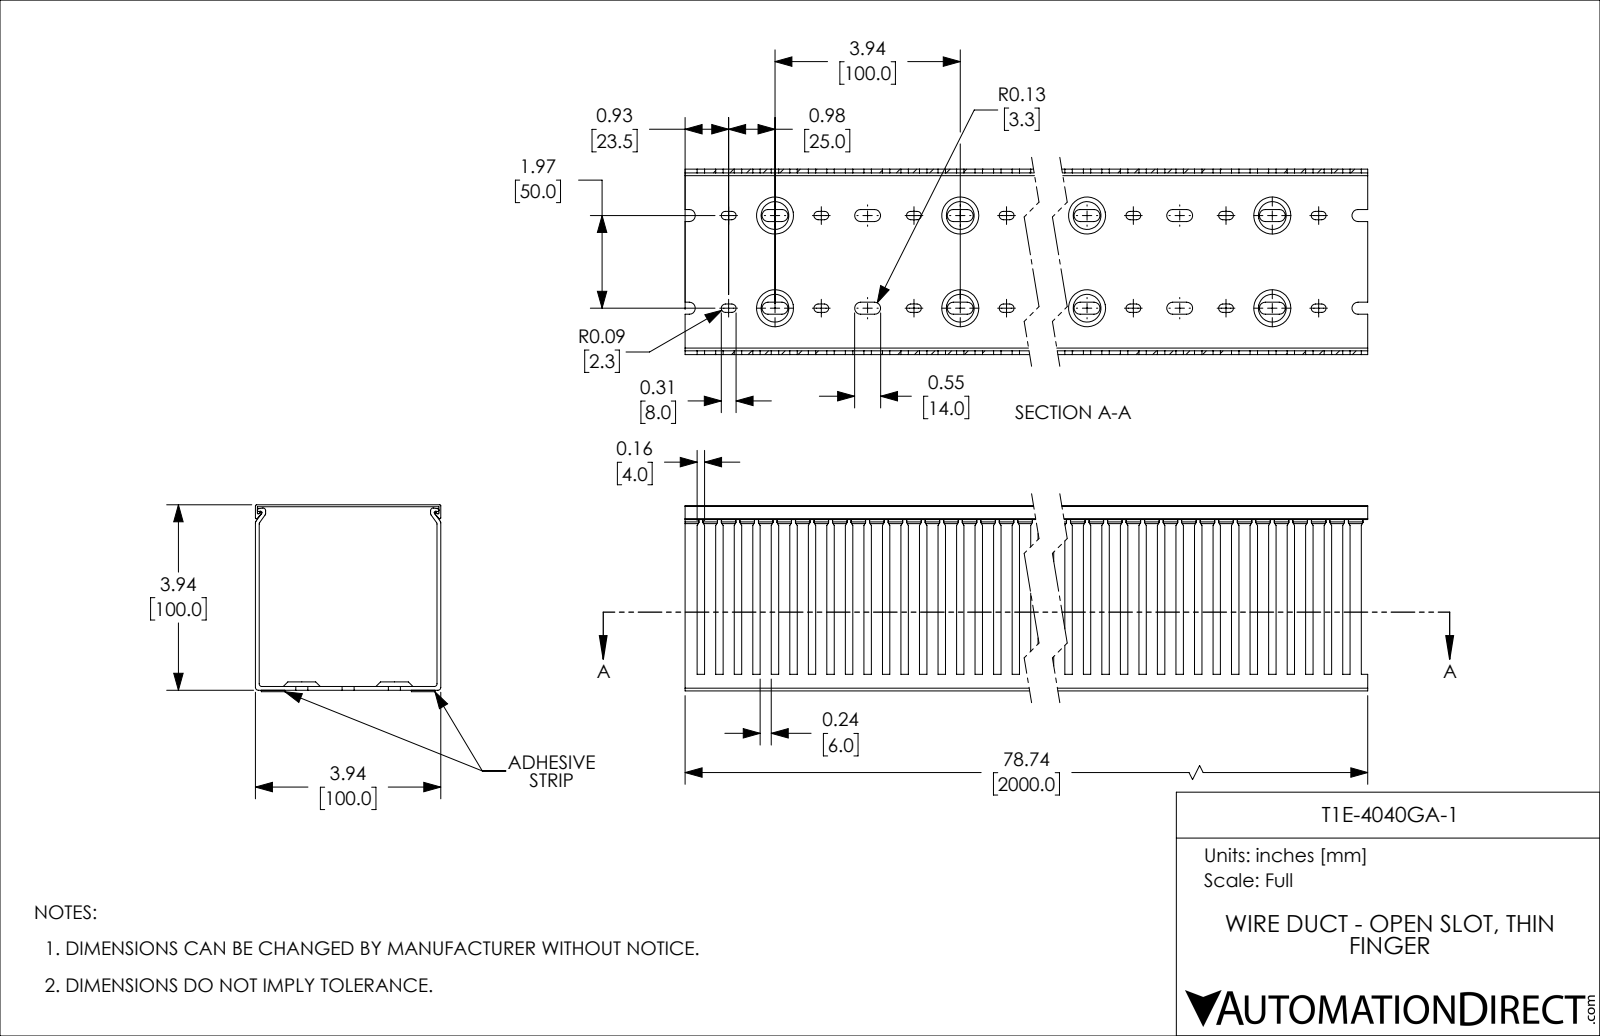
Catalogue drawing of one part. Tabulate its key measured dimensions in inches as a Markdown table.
| quantity | value |
| --- | --- |
| part name | T1E-4040GA-1 |
| STEP written by | SolidWorks 2021 (CONFIG_CONTROL_DESIGN) |
| units | inches |
| bodies | 4 solids, 1585 faces (774 planar, 731 cylindrical, 80 other) |
| overall size | 78.74 × 3.968 × 3.937 |
| volume | 88.55 in³ |
| surface area | 2 728 in² |
| partial cylindrical surfaces (radius × count) | 0.128 × 200, 0.089 × 160, 0.059 × 12, 0.02 × 8, 0.03 × 6 |
| main face-to-face distances | 0.079, 3.858, 3.937, 0.039, 3.898, 3.819, 3.78, 0.031, 0.11, 3.929 |
